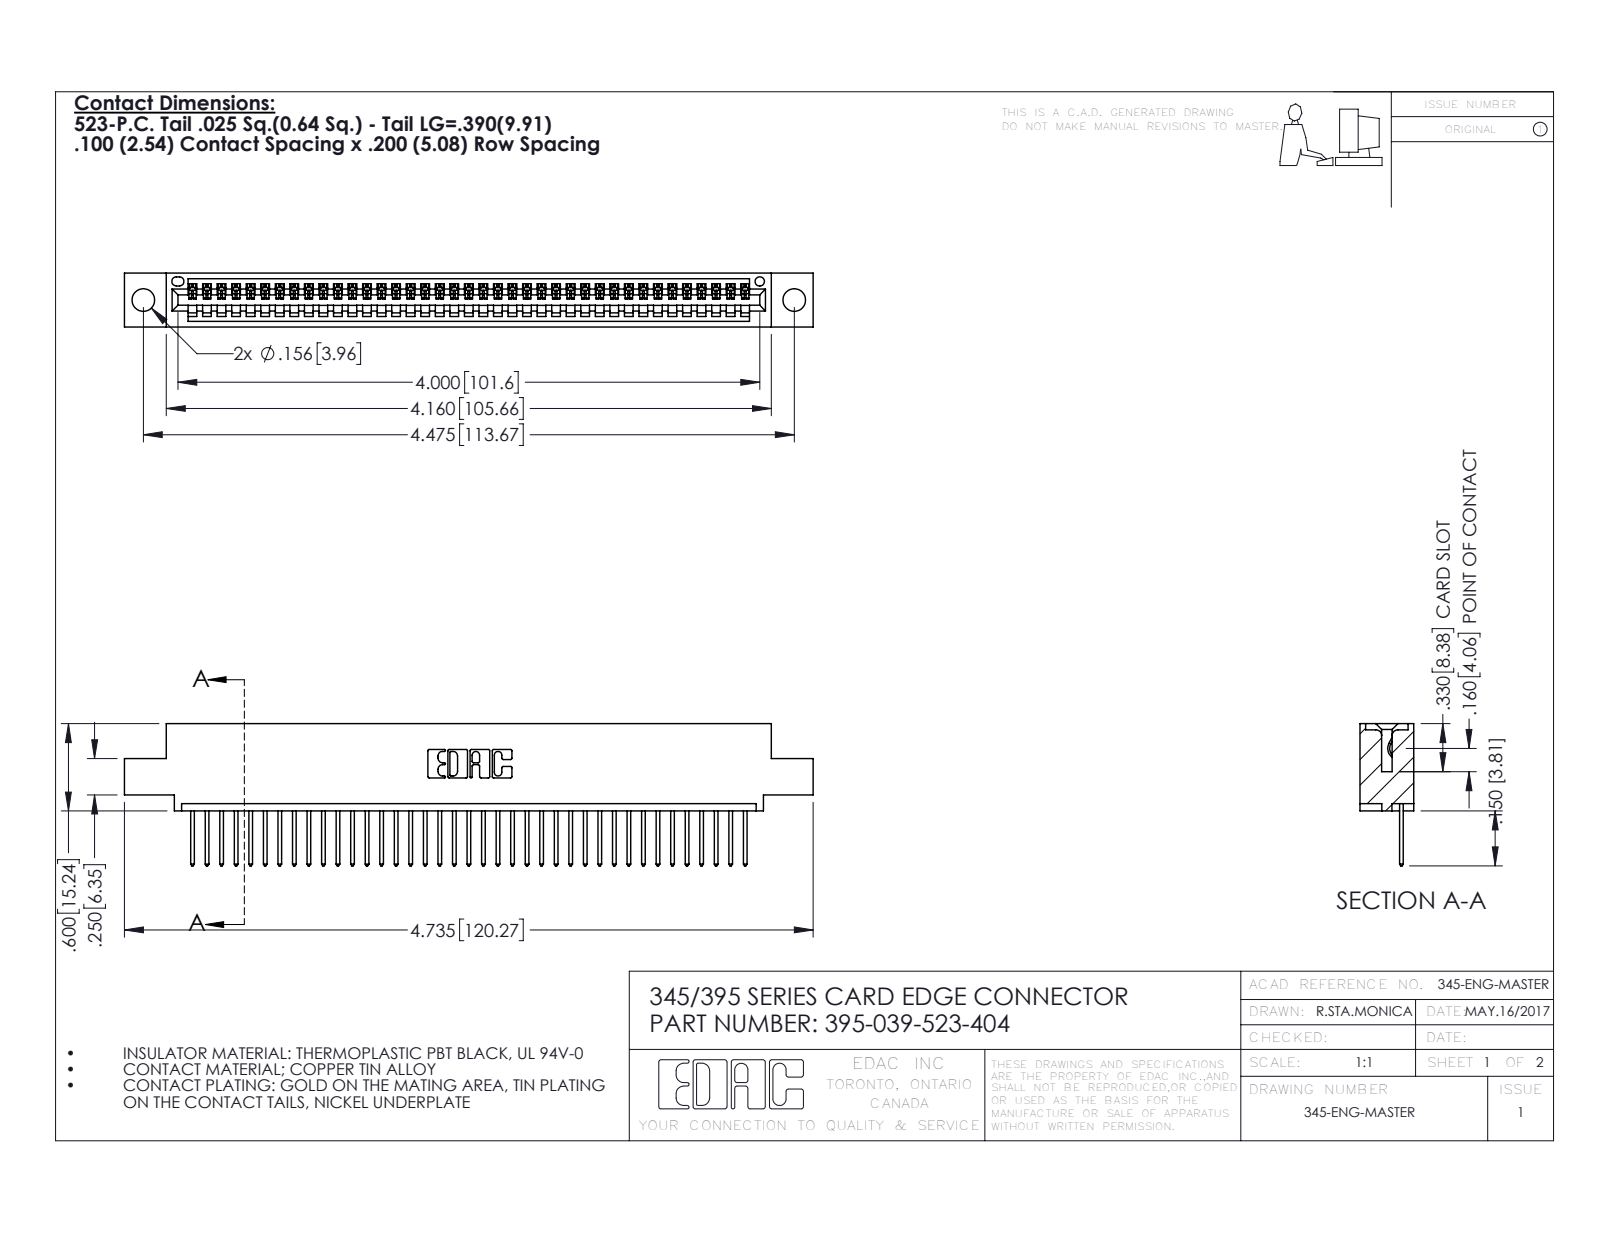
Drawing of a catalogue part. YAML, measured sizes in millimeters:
part_name: "345 Part_0.110 Offset - 0.156 Dia-TH; 395-039-523-404; 345-292-001_345-293-123"
step_written_by: "SolidWorks 2016 (CONFIG_CONTROL_DESIGN)"
units: millimeters
bodies: {solids: 40, faces: 2392, planar: 1644, cylindrical: 748, other: 0}
overall_size: [120.3, 24.8, 9.4]
volume: 11200
surface_area: 14810
round_holes:
  - {diameter: 4, count: 2}
  - {diameter: 1.6, count: 1}
partial_cylinders:
  - {radius: 0.2, count: 78}
  - {radius: 0.3, count: 78}
  - {radius: 0.3, count: 22}
  - {radius: 0.2, count: 6}
  - {radius: 0.8, count: 6}
  - {radius: 0.7, count: 3}
  - {radius: 0.8, count: 2}
  - {radius: 1, count: 2}
face_to_face_distances: [7.6, 1.8, 9.4, 2.5, 6.9, 0.6, 5.1, 5.7, 3.8, 1.8]
hole_center_spacings: [6.9, 107.7, 113.7]
